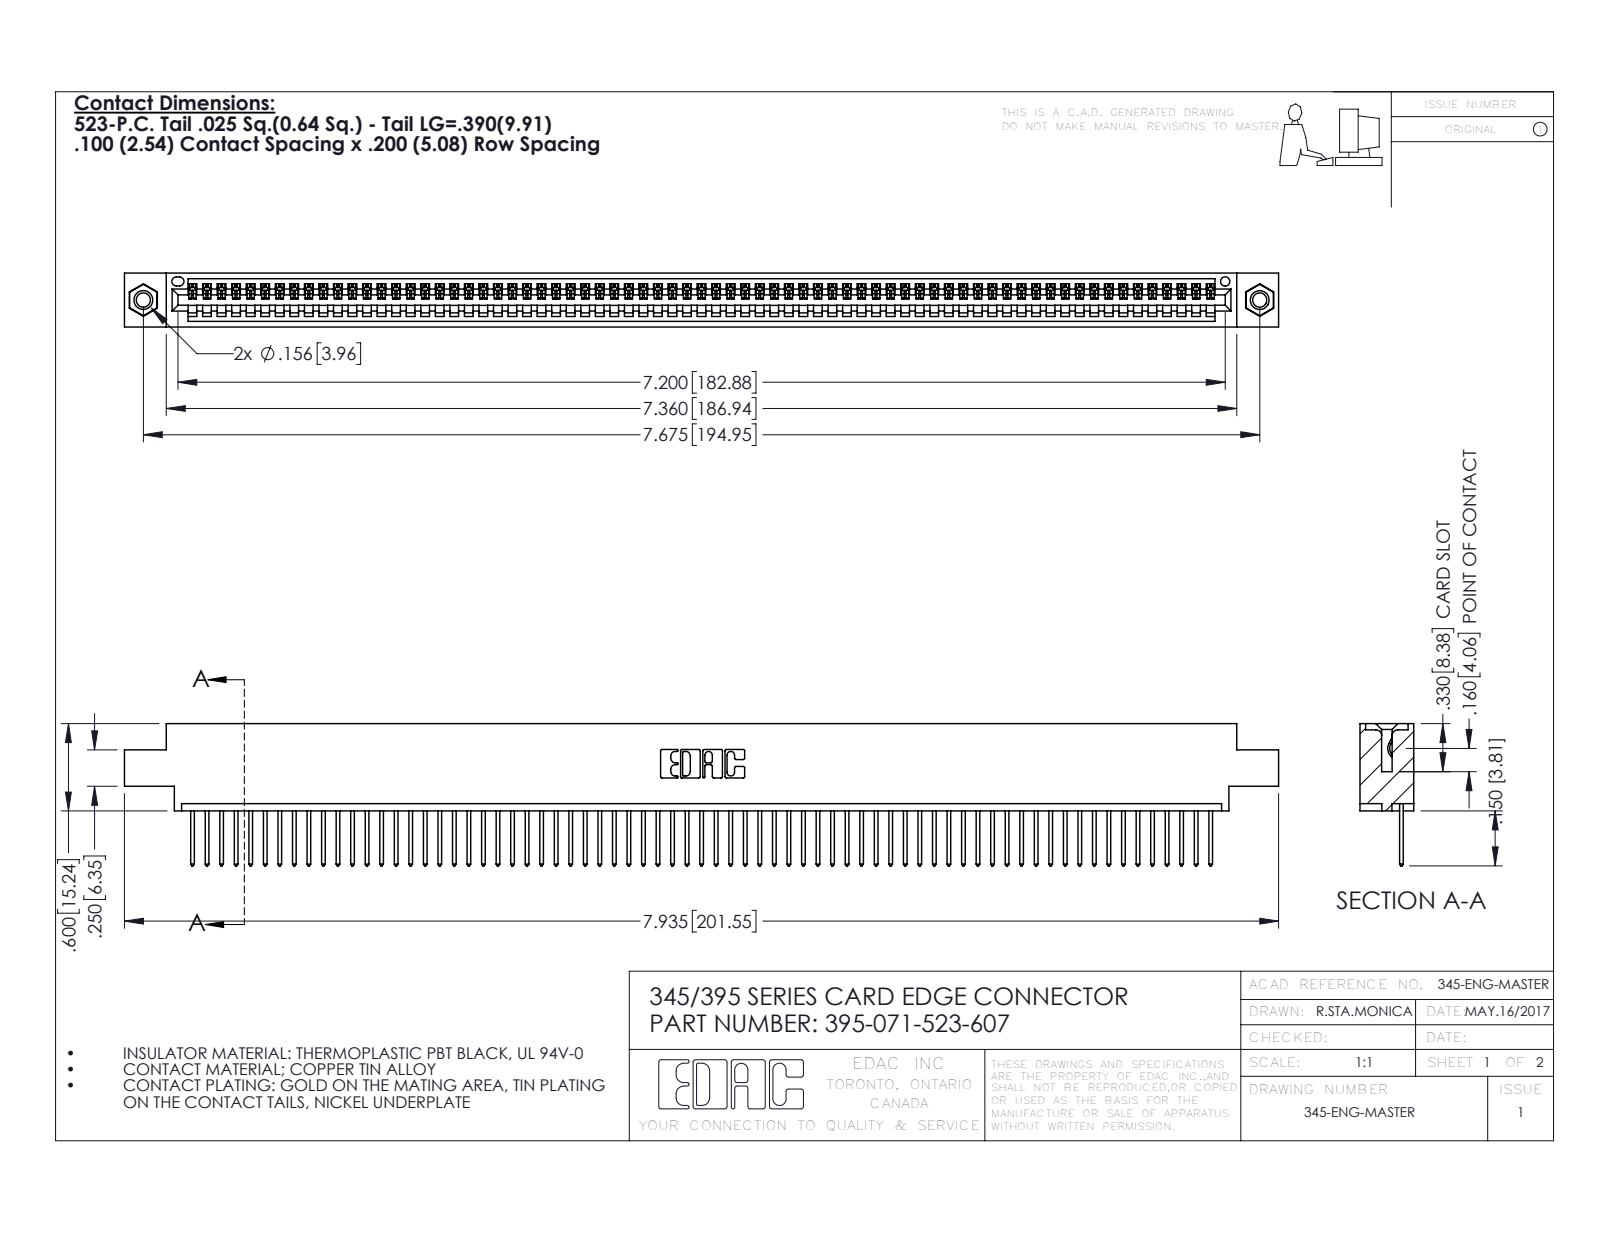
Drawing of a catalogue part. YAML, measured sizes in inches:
part_name: "345 Part_0.170 Offset - 0.156 Dia-TI; 345-292-001_345-293-123; 345-250-001_345-250-005-103; 395-071-523-607"
step_written_by: "SolidWorks 2016 (CONFIG_CONTROL_DESIGN)"
units: inches
bodies: {solids: 74, faces: 4308, planar: 2956, cylindrical: 1336, other: 16}
overall_size: [7.935, 0.977, 0.37]
volume: 1.173
surface_area: 40.58
round_holes:
  - {diameter: 0.098, count: 2}
  - {diameter: 0.125, count: 2}
  - {diameter: 0.156, count: 2}
  - {diameter: 0.064, count: 1}
round_bosses_or_shafts:
  - {diameter: 0.155, count: 2}
partial_cylinders:
  - {radius: 0.006, count: 142}
  - {radius: 0.01, count: 142}
  - {radius: 0.01, count: 22}
  - {radius: 0.007, count: 6}
  - {radius: 0.031, count: 6}
  - {radius: 0.026, count: 3}
  - {radius: 0.031, count: 2}
  - {radius: 0.04, count: 2}
face_to_face_distances: [0.072, 0.298, 0.37, 0.098, 0.272, 0.025, 0.2, 0.225, 0.175, 0.149]
hole_center_spacings: [0.27, 7.439, 7.675]
